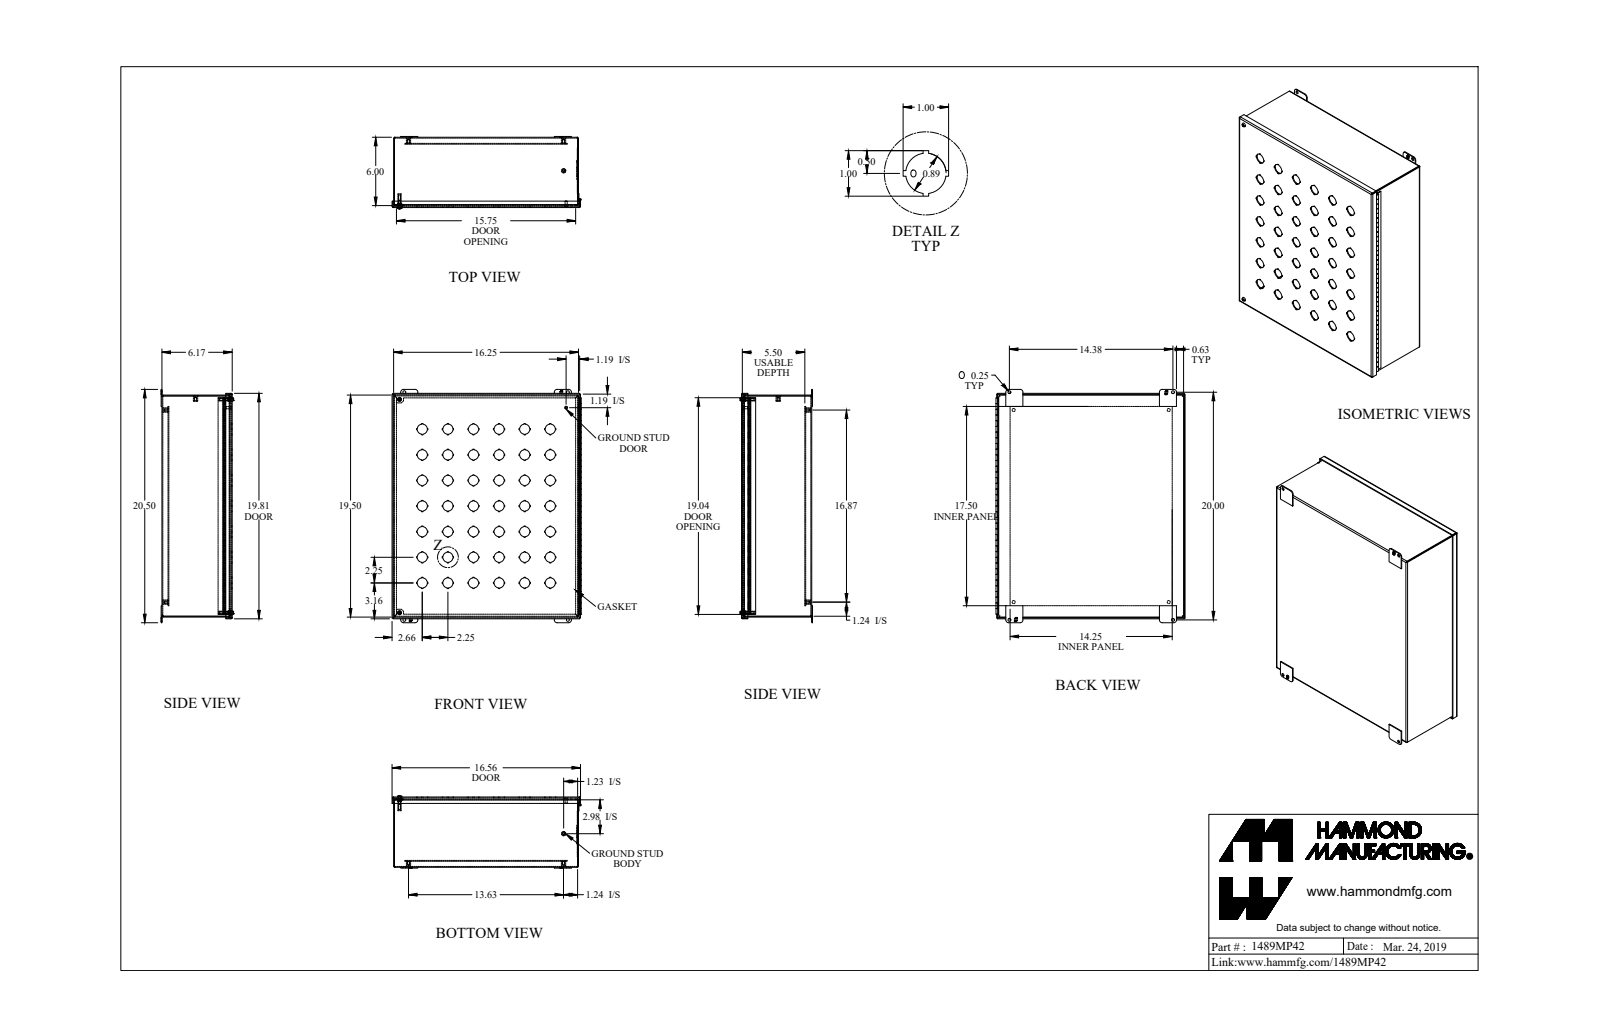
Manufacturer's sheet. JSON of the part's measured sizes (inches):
{"part_name": "1489MP42_Default", "step_written_by": "SolidWorks 2019 (CONFIG_CONTROL_DESIGN)", "units": "inches", "bodies": {"solids": 21, "faces": 1506, "planar": 1063, "cylindrical": 385, "other": 58}, "overall_size": [20.5, 16.623, 6.371], "volume_in3": 107.5, "surface_area_in2": 2901, "round_holes": [[0.886, 42], [0.25, 6], [0.156, 5], [0.265, 4], [0.159, 2], [0.406, 2]], "round_bosses_or_shafts": [[0.375, 5], [0.39, 2], [0.275, 2], [0.19, 2], [0.148, 2], [0.25, 1], [0.188, 1], [0.174, 1]], "partial_cylinders_radius": [[0.036, 12], [0.108, 12], [0.25, 8], [0.16, 2], [0.171, 2], [0.125, 1]], "face_to_face_distances": [0.072, 6.1, 5.568, 0.532, 6.028, 6.172, 0.604, 5.64, 0.46, 5.496], "hole_center_spacings": [5.031, 2.25, 3.182, 7.115, 4.5, 8.113, 6.75, 6.364]}
